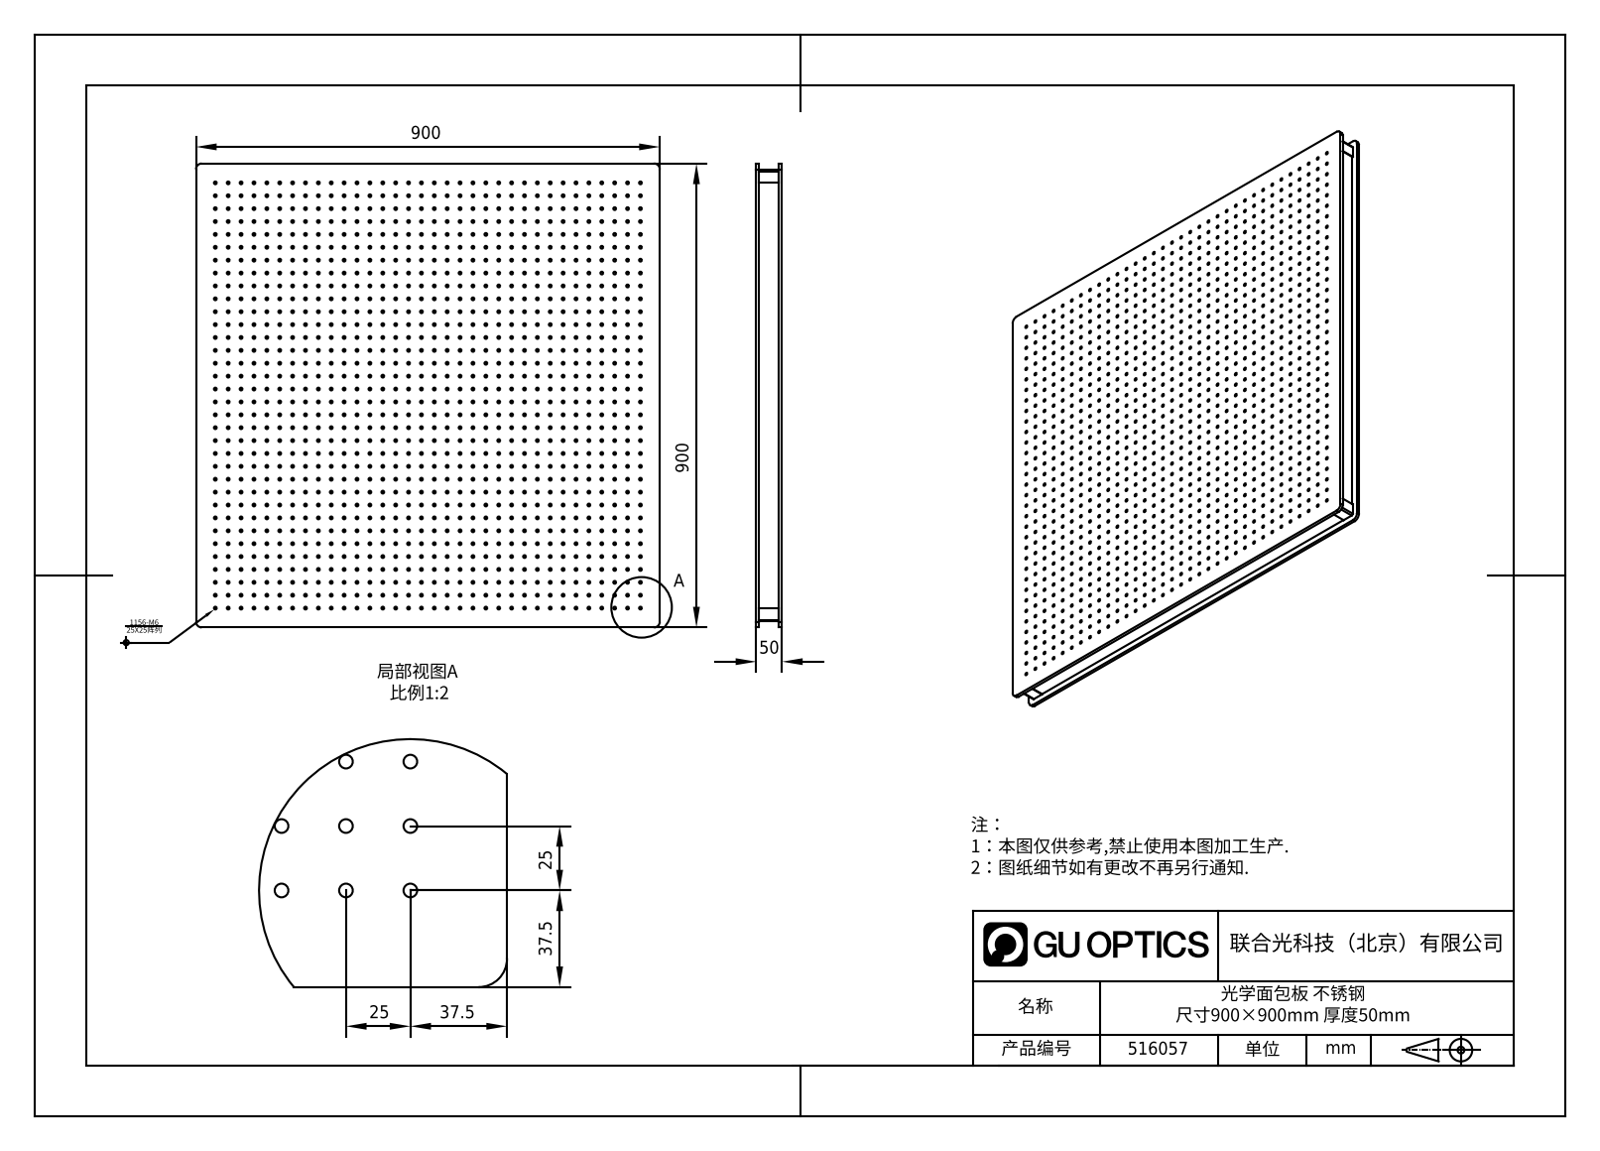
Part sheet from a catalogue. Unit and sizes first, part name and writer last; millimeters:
Units: millimetres
Overall size (bounding box): 900 × 900 × 50
Round holes (diameter × count): ⌀5.3 ×1156
Partial cylindrical surfaces — rounded edges, fillets, slot ends (radius × count): R2 ×4, R3 ×4, R11 ×4
Main face-to-face distances: 50, 6, 44, 874, 45, 39, 5, 13, 887, 900
Hole centre spacings: 50, 100, 35.36, 79.06, 150, 127.48, 176.78, 200
Volume: 38 550 000 mm³ · Surface area: 2 011 000 mm²
Bodies: 1 solid, 3528 faces (1200 planar, 2328 cylindrical, 0 other)
Part name (STEP PRODUCT): 516057
STEP written by: SolidWorks 2020 (CONFIG_CONTROL_DESIGN)
